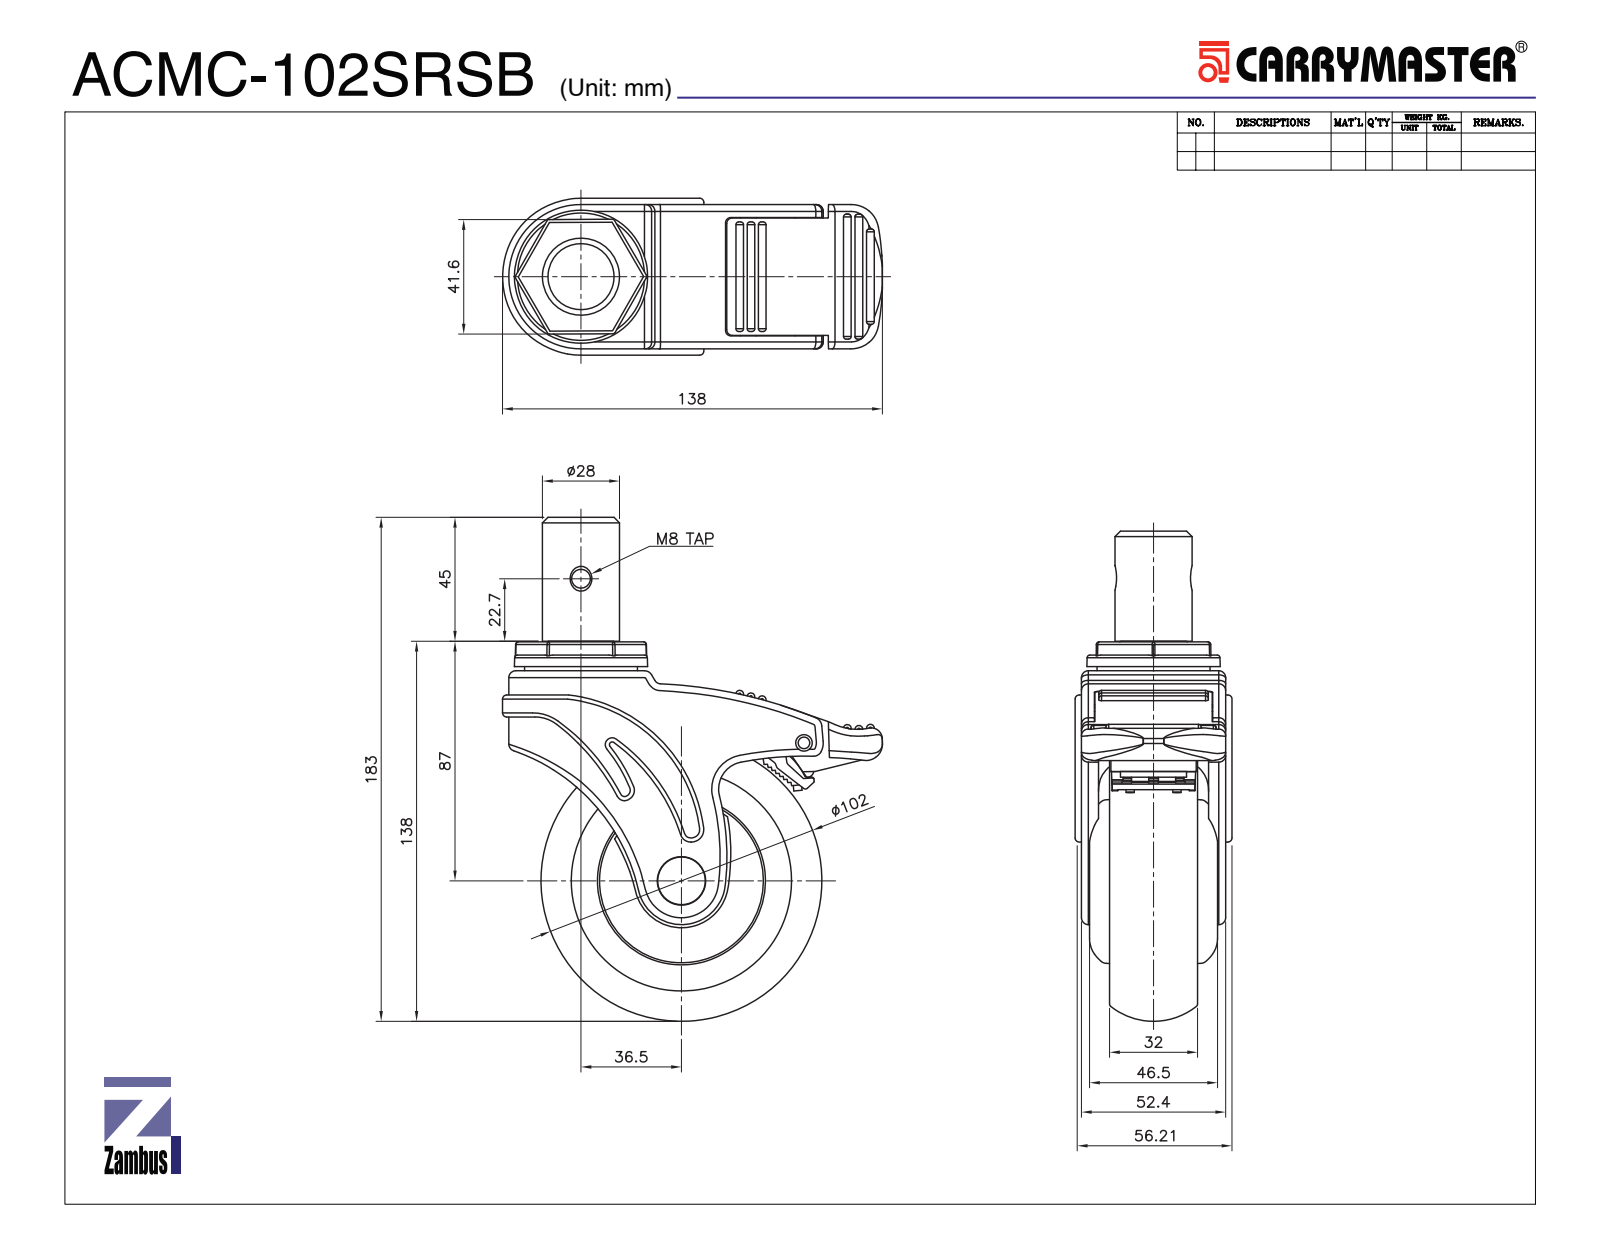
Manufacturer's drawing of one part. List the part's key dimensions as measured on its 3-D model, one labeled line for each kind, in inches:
Part name (STEP PRODUCT): ACMC-102 TOP PLATE COVER; ACMC-102 SRS TOP PLATE; ACMC-102 WHEEL; 09. ACMC-102SRSB (+2 more)
STEP written by: SolidWorks 2019 (CONFIG_CONTROL_DESIGN)
Units: inches
Bodies: 6 solids, 672 faces (216 planar, 277 cylindrical, 179 other)
Overall size (bounding box): 7.201 × 5.421 × 2.22
Volume: 27.51 in³ · Surface area: 138 in²
Round holes (diameter × count): ⌀0.268 ×1, ⌀0.315 ×1, ⌀0.681 ×1, ⌀1.417 ×1, ⌀1.591 ×1, ⌀2.402 ×1, ⌀3.15 ×1
Round bosses / shafts (diameter × count): ⌀0.157 ×2, ⌀3.15 ×1, ⌀2.362 ×1, ⌀2.343 ×1, ⌀1.614 ×1, ⌀1.102 ×1, ⌀0.866 ×1, ⌀0.669 ×1
Partial cylindrical surfaces — rounded edges, fillets, slot ends (radius × count): R0.02 ×27, R0.039 ×16, R0.098 ×7, R0.055 ×6, R0.079 ×6, R0.059 ×4, R0.118 ×3, R0.394 ×3
Main face-to-face distances: 0.165, 1.425, 0.236, 1.661, 0.402, 1.827, 1.591, 1.26, 2.063, 0.246
Hole centre spacings: 4.548, 4.552
